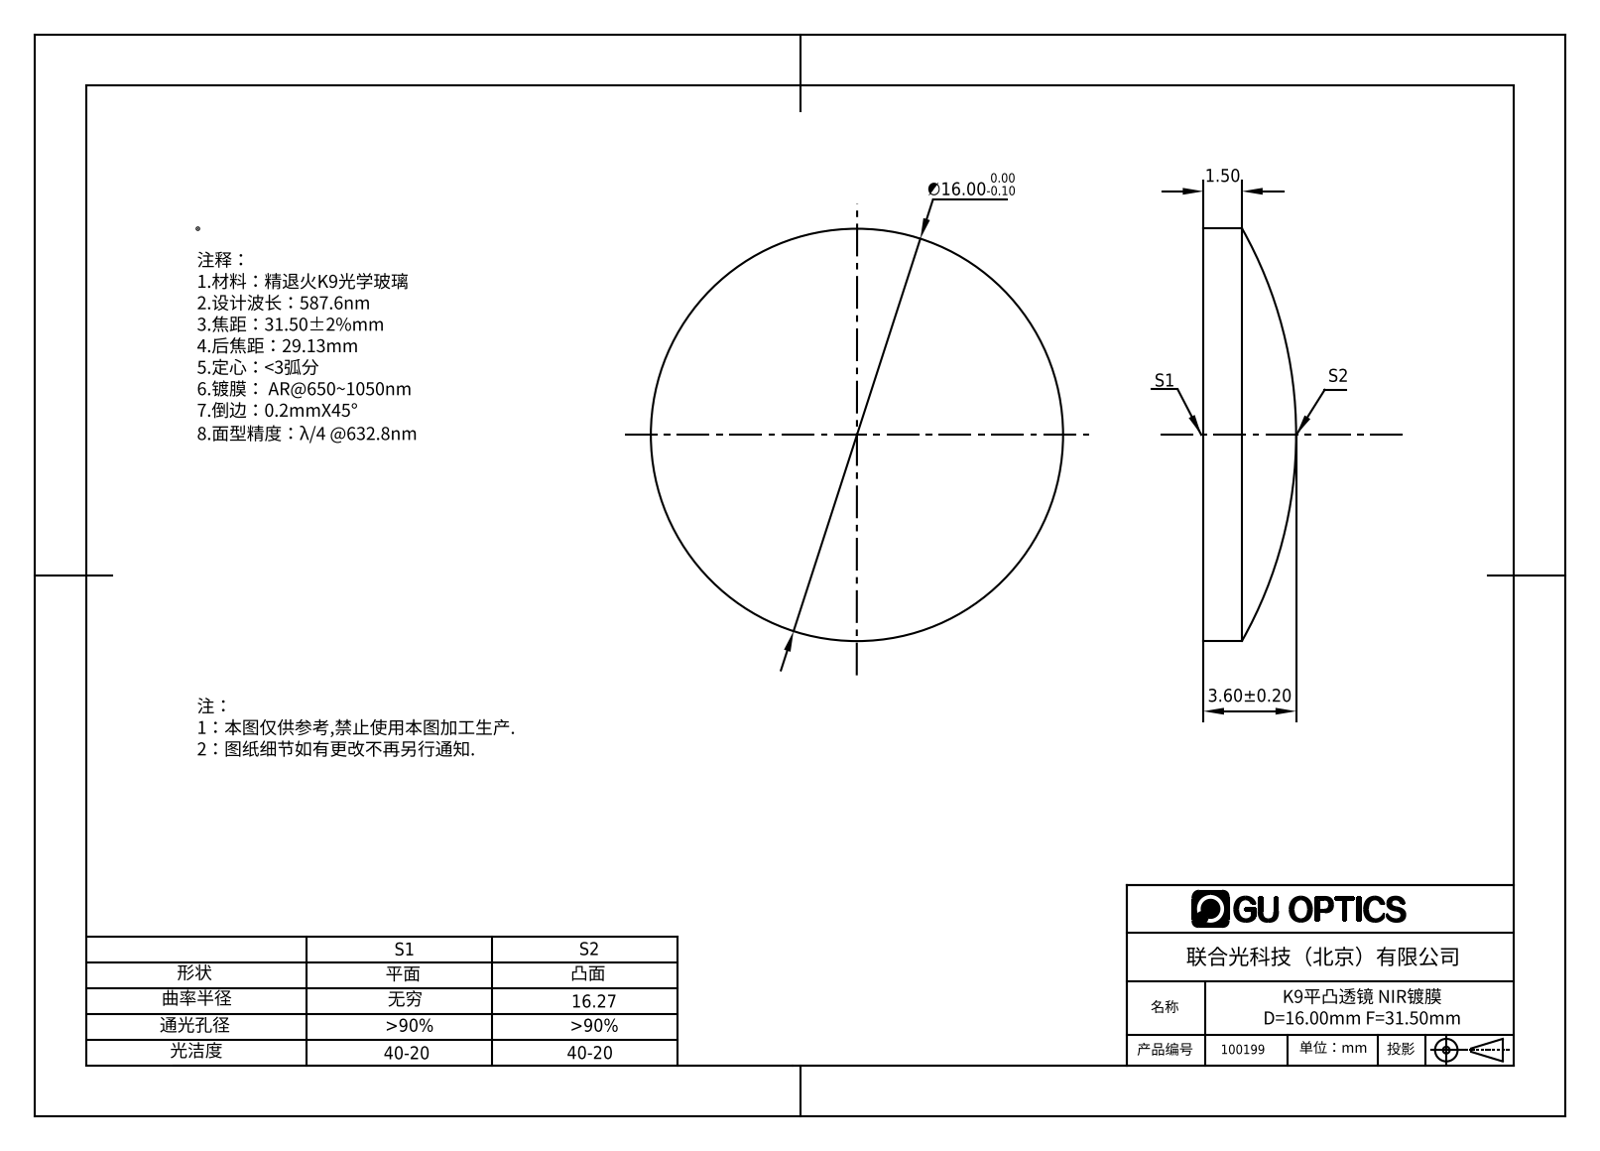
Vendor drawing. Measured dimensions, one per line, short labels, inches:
name: 100199
written by: SolidWorks 2016 (AUTOMOTIVE_DESIGN)
unit: in
bodies: 1 solid, 5 faces (1 planar, 2 cylindrical, 2 other)
size: 0.63 × 0.63 × 0.142
volume: 0.032 in³; area: 0.761 in²
bosses: 1× ⌀0.63
